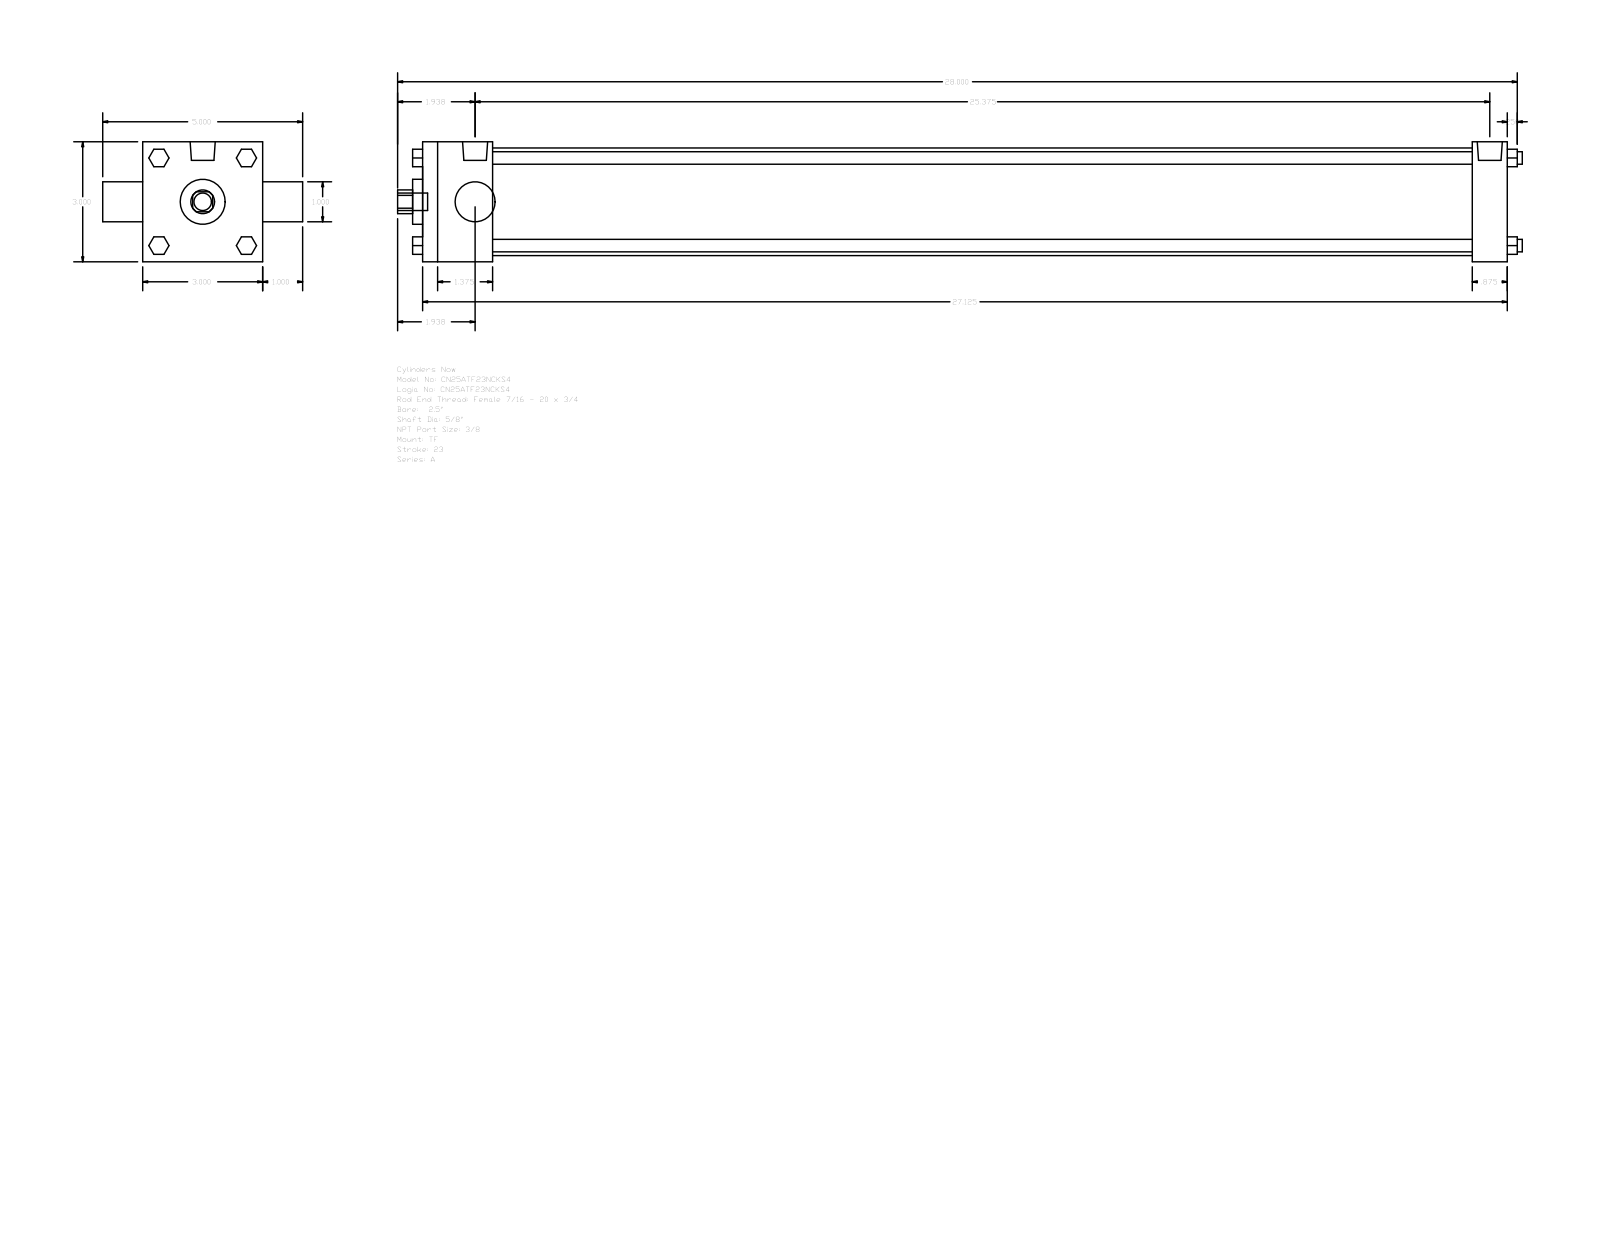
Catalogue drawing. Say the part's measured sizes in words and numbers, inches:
The part is named "A_TF__0250_0.625". Its 3-D file was written by "GSSL Pune (CONFIG_CONTROL_DESIGN)". It is 0 solids with 120 faces: 92 planar, 28 cylindrical and 0 other. Overall it measures 28.125 by 5 by 3 inches. Round holes: 1 of diameter 0.625, 1 of diameter 1, 1 of diameter 1.125, 1 of diameter 2.69. Round bosses or shafts: 4 of diameter 0.313, 3 of diameter 0.219, 2 of diameter 0.627, 1 of diameter 0.437. Partial cylindrical surfaces (rounded edges, fillets, slot ends): 1 of radius 0.297. The main face-to-face distances are 3, 27.125, 1.75, 26.25, 24.5, 25.375, 0.875, 1, 4, 0.25.
